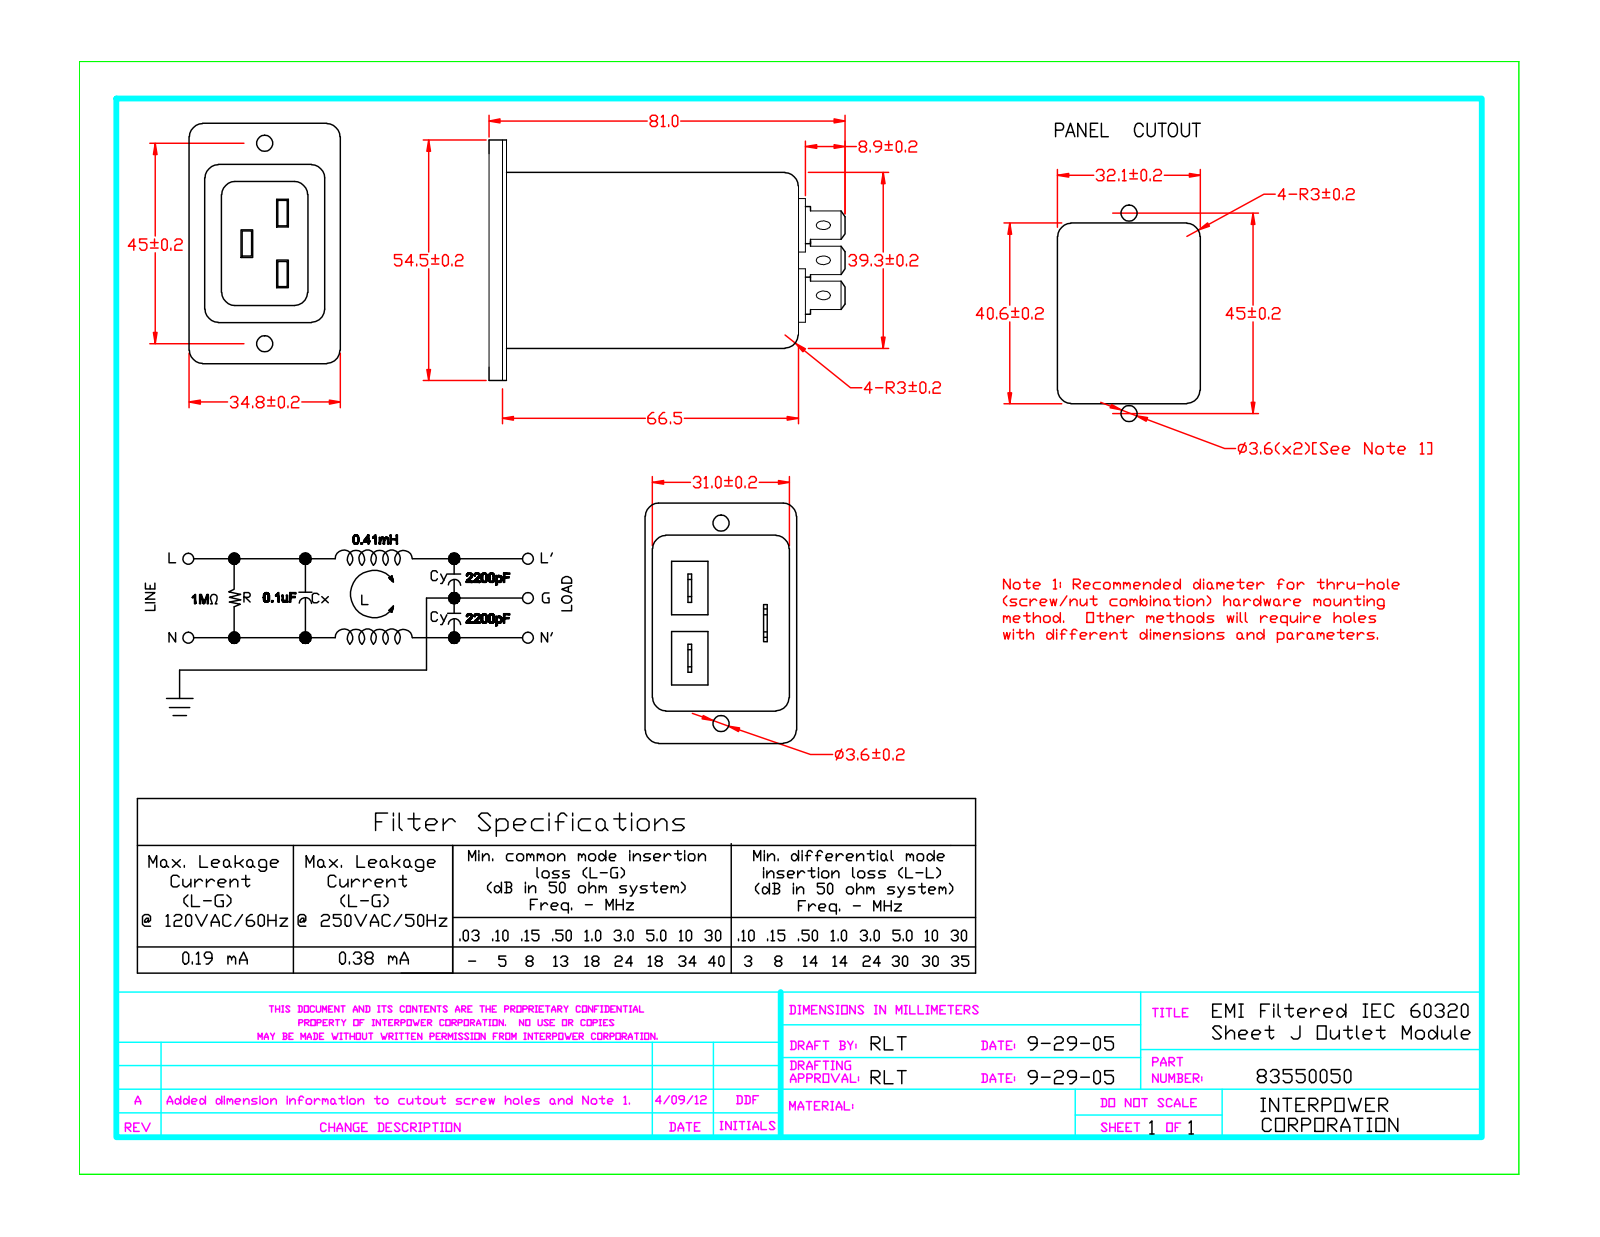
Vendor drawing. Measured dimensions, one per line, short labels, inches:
name: 83550050
written by: SolidWorks 2007 (CONFIG_CONTROL_DESIGN)
unit: in
bodies: 1 solid, 137 faces (87 planar, 36 cylindrical, 14 other)
size: 3.189 × 2.146 × 1.37
volume: 4.776 in³; area: 32.21 in²
holes: 2× ⌀0.144
rounds: 20× R0.118
face distances: 1.22, 1.547, 0.15, 0.075, 0.079, 1.142, 0.228, 0.992, 0.913, 1.472
hole spacings: 1.772
